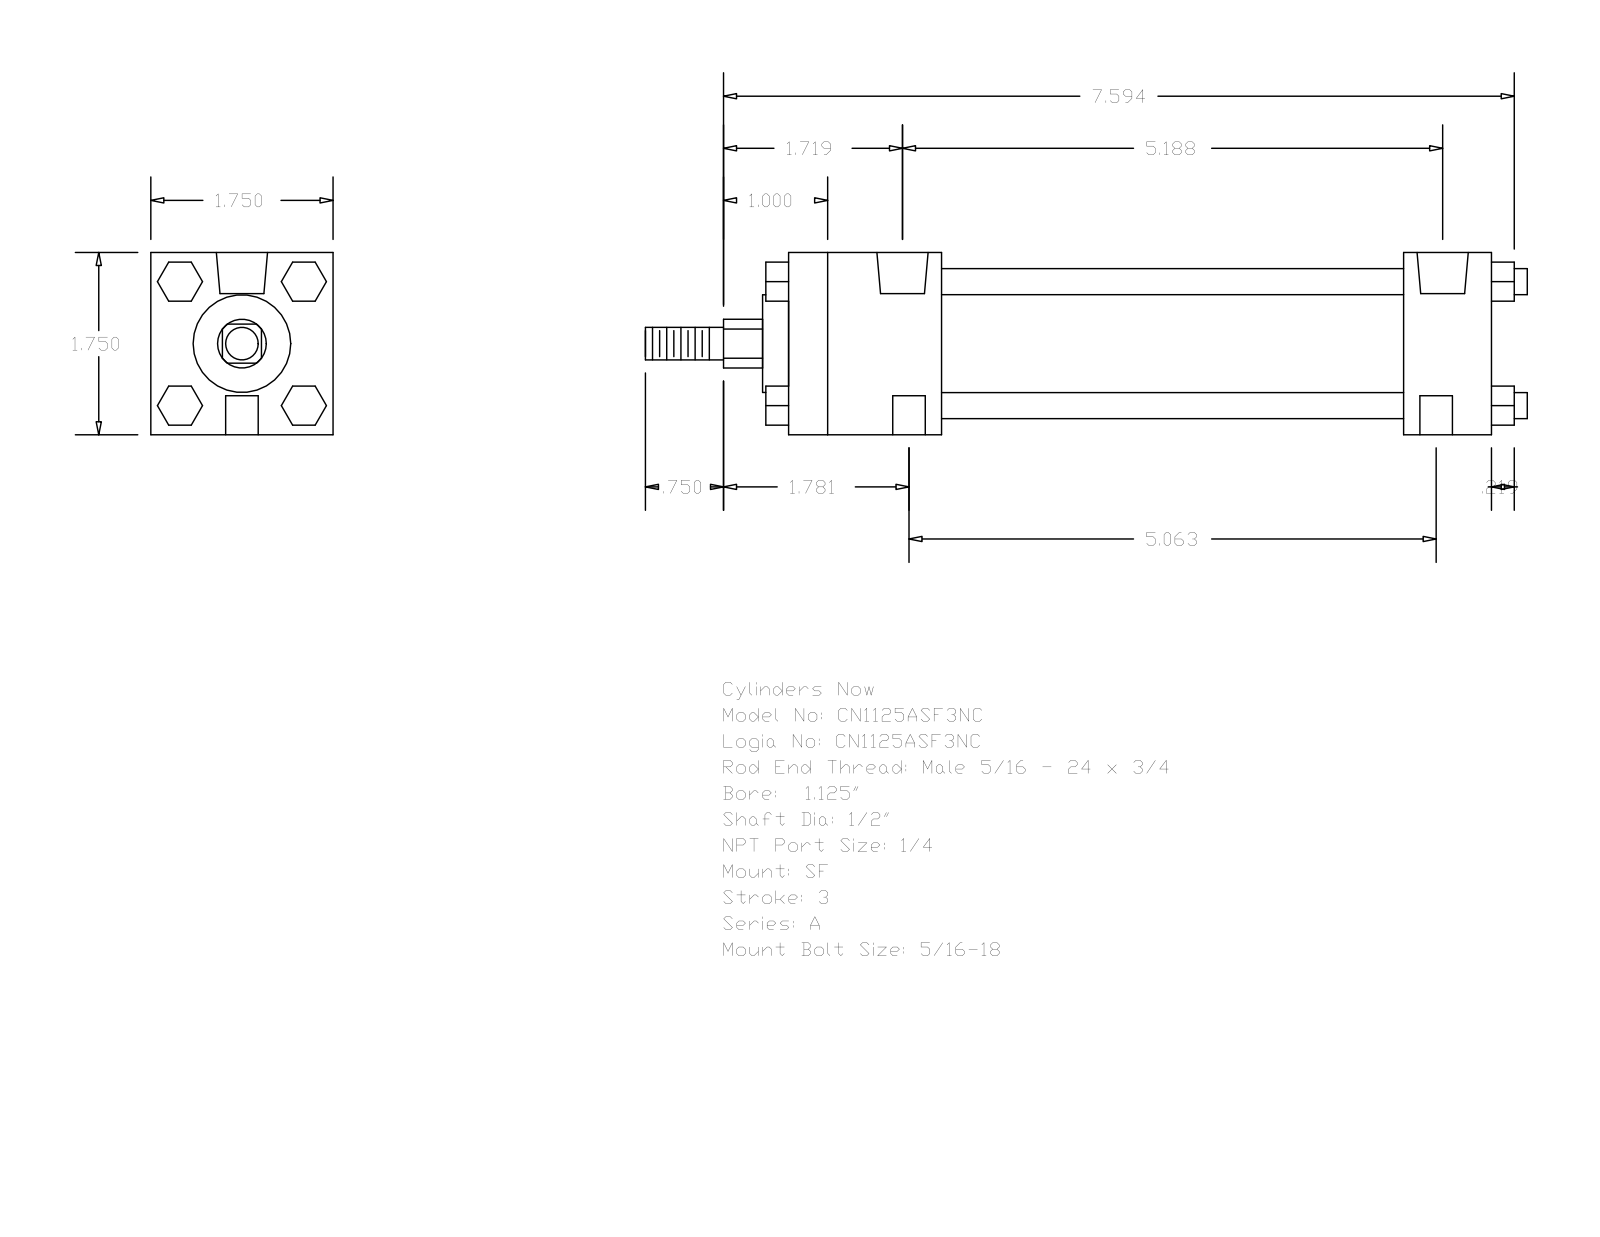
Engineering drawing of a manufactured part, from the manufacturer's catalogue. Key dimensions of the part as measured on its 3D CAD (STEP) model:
Part name (STEP PRODUCT): A_SF__0112_0.5
STEP written by: GSSL Pune (CONFIG_CONTROL_DESIGN)
Units: millimetres
Bodies: 0 solids, 120 faces (92 planar, 28 cylindrical, 0 other)
Overall size (bounding box): 215.11 × 44.45 × 44.45
Round holes (diameter × count): ⌀5.56 ×2, ⌀7.94 ×2, ⌀12.49 ×2
Round bosses / shafts (diameter × count): ⌀6.35 ×4, ⌀31.88 ×1, ⌀23.81 ×1, ⌀12.7 ×1, ⌀7.94 ×1
Partial cylindrical surfaces — rounded edges, fillets, slot ends (radius × count): R5.94 ×1
Main face-to-face distances: 44.46, 171.44, 150.01, 21.43, 37.3, 112.71, 134.14, 9.53, 5.59, 5.56
Hole centre spacings: 128.59, 1.58, 1.59, 130.17, 130.18, 131.76
